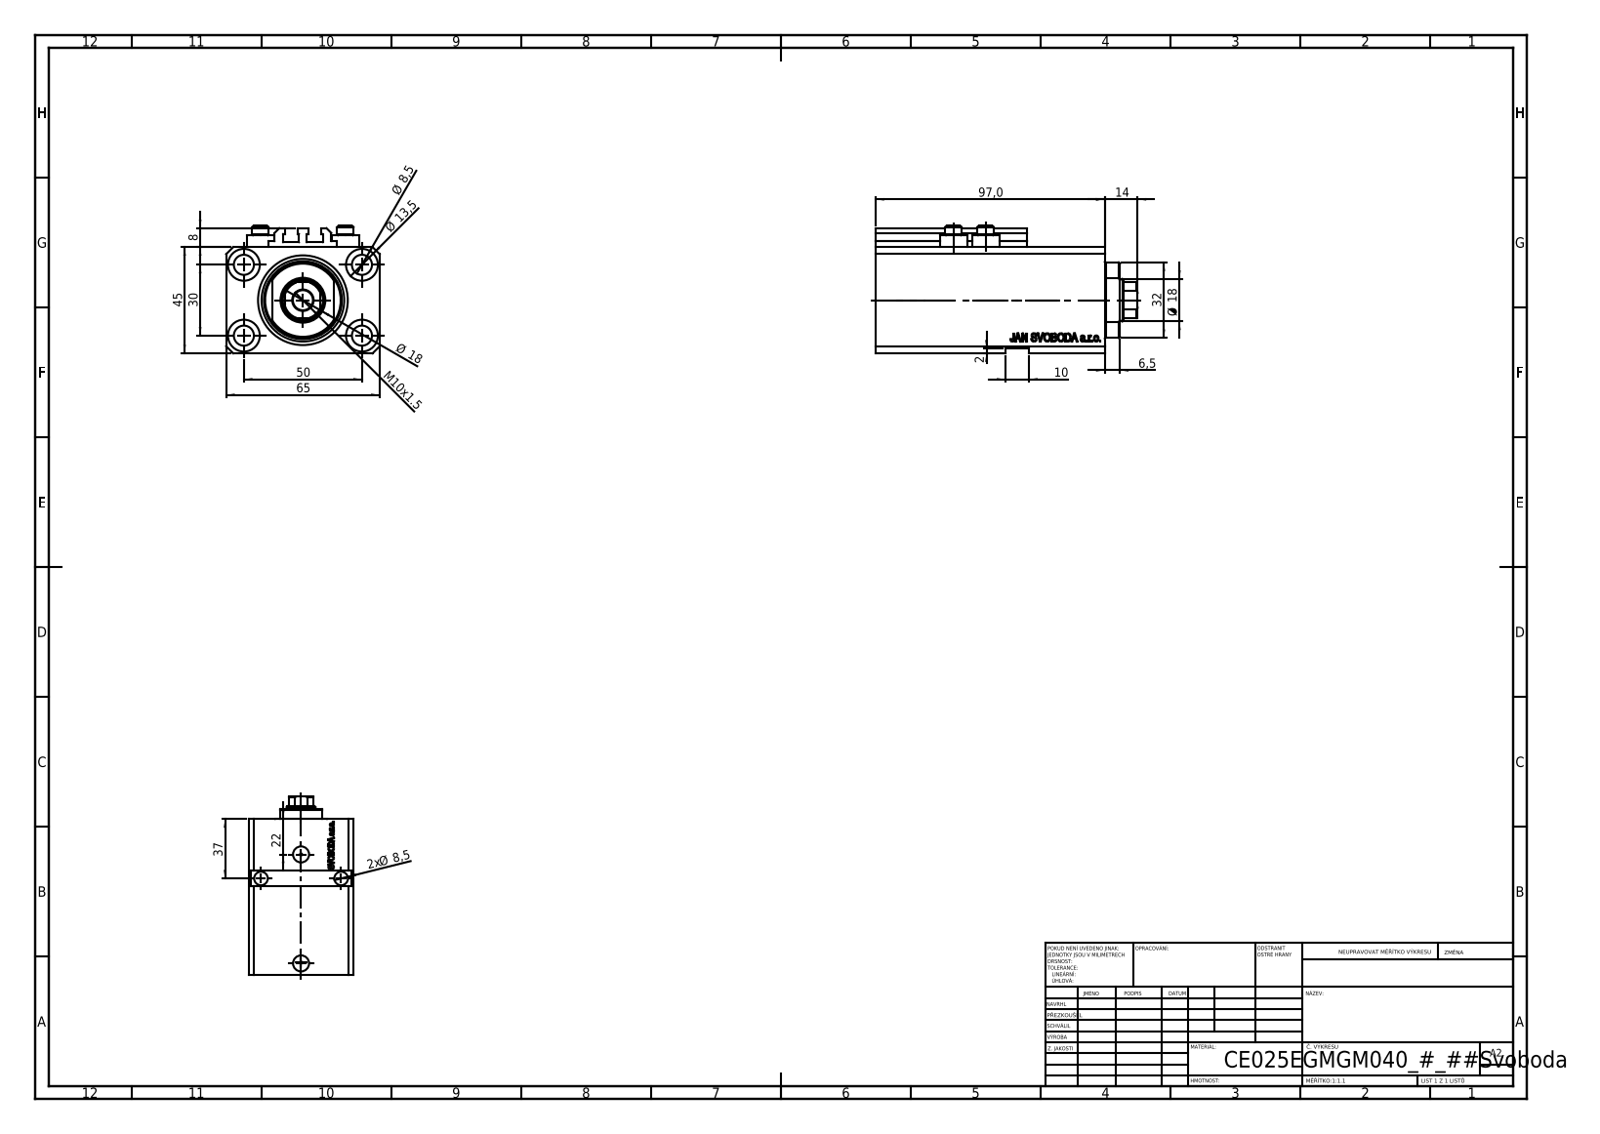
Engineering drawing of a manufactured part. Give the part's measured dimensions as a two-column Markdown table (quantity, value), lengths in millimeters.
| quantity | value |
| --- | --- |
| part name | V250CE_C_VCP; V250CE_E_Body; V250CE_VC_E; ALLEN BOLT V250CE |
| STEP written by | SolidWorks 2019 (CONFIG_CONTROL_DESIGN) |
| units | millimeters |
| bodies | 8 solids, 1067 faces (511 planar, 126 cylindrical, 430 other) |
| overall size | 111 × 65 × 54 |
| volume | 251 171 mm³ |
| surface area | 70 299 mm² |
| round holes (diameter × count) | 8.5 × 7, 1.25 × 4, 4 × 4, 13.5 × 4, 10 × 2, 13.16 × 2, 20 × 2, 18 × 1, 25 × 1, 38 × 1 |
| round bosses / shafts (diameter × count) | 11.6 × 4, 7 × 4 |
| partial cylindrical surfaces (radius × count) | 0.2 × 10, 8.5 × 1, 16 × 1 |
| main face-to-face distances | 45, 65, 83, 14, 2, 97, 47, 6.9, 76.1, 90.1 |
| hole center spacings | 29.15, 50, 13.6, 15.12, 27.89, 30, 31.19, 31.62 |
